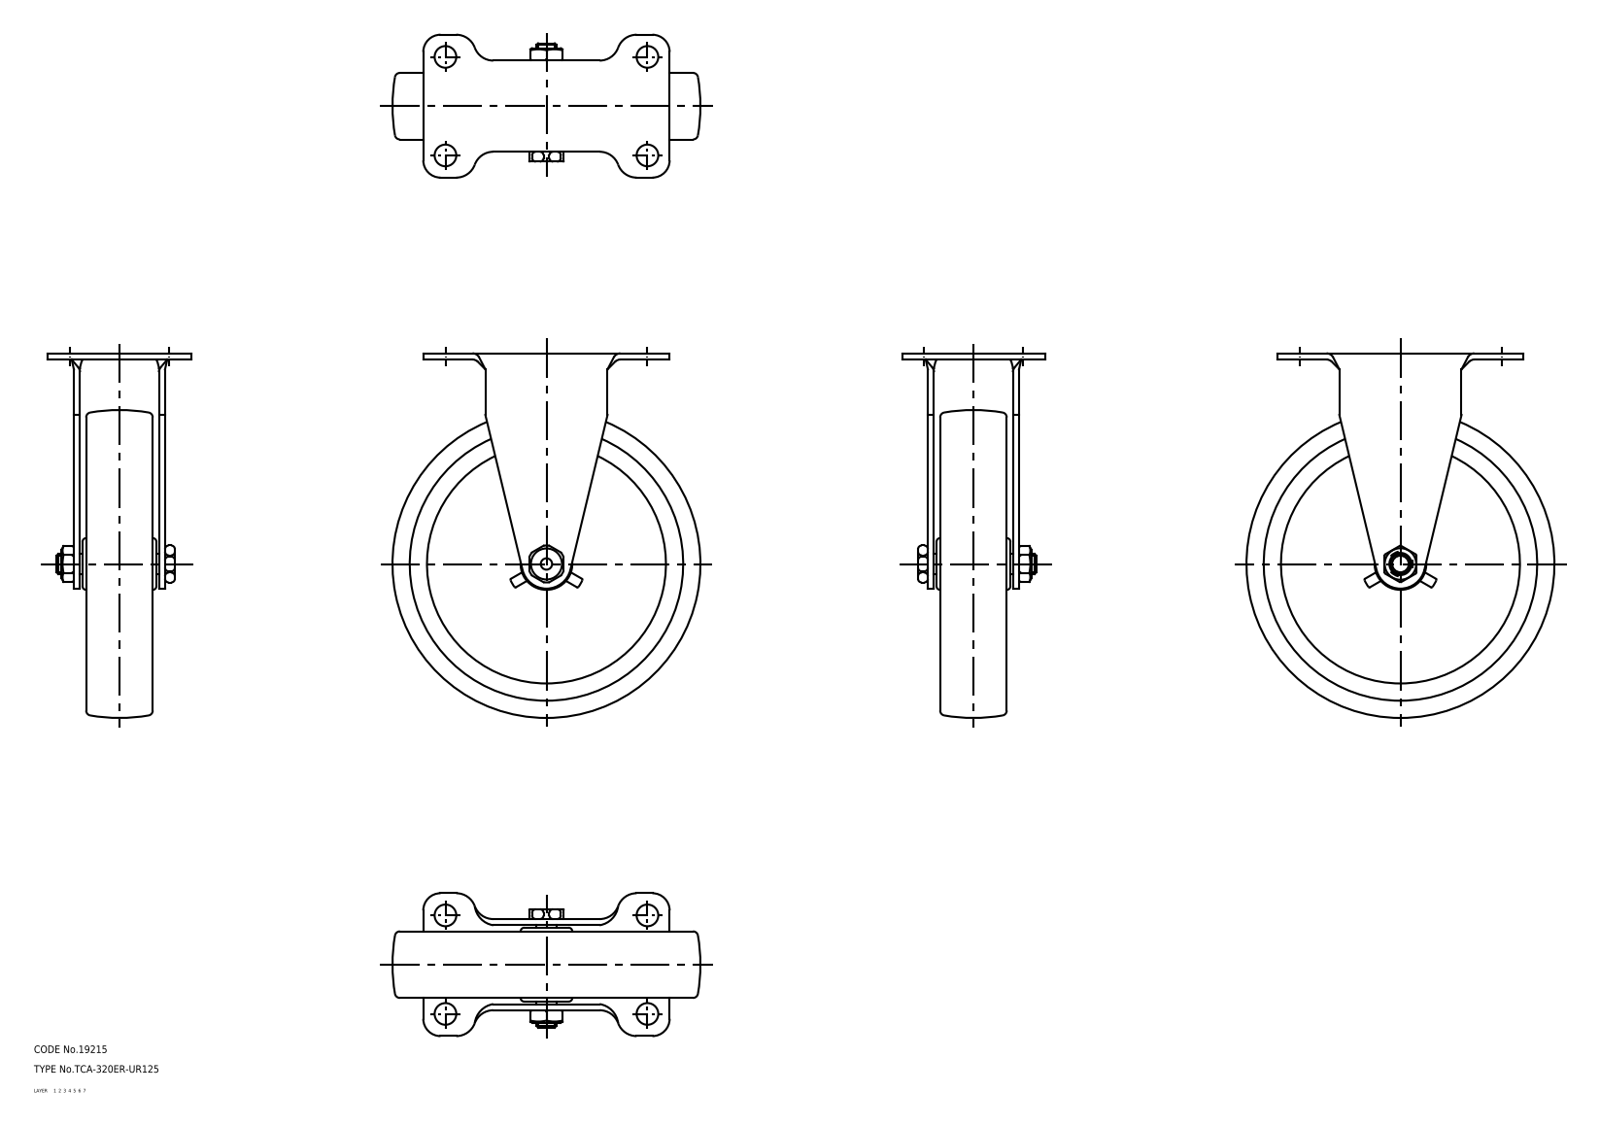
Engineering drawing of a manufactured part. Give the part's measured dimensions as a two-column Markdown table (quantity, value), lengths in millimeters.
| quantity | value |
| --- | --- |
| part name | wheel; axle; 320ER_UR125_3577_36 |
| STEP written by | CADfix (AUTOMOTIVE_DESIGN) |
| units | millimeters |
| bodies | 3 solids, 271 faces (0 planar, 0 cylindrical, 271 other) |
| overall size | 148 × 125 × 58 |
| volume | 270 624 mm³ |
| surface area | 63 546 mm² |
